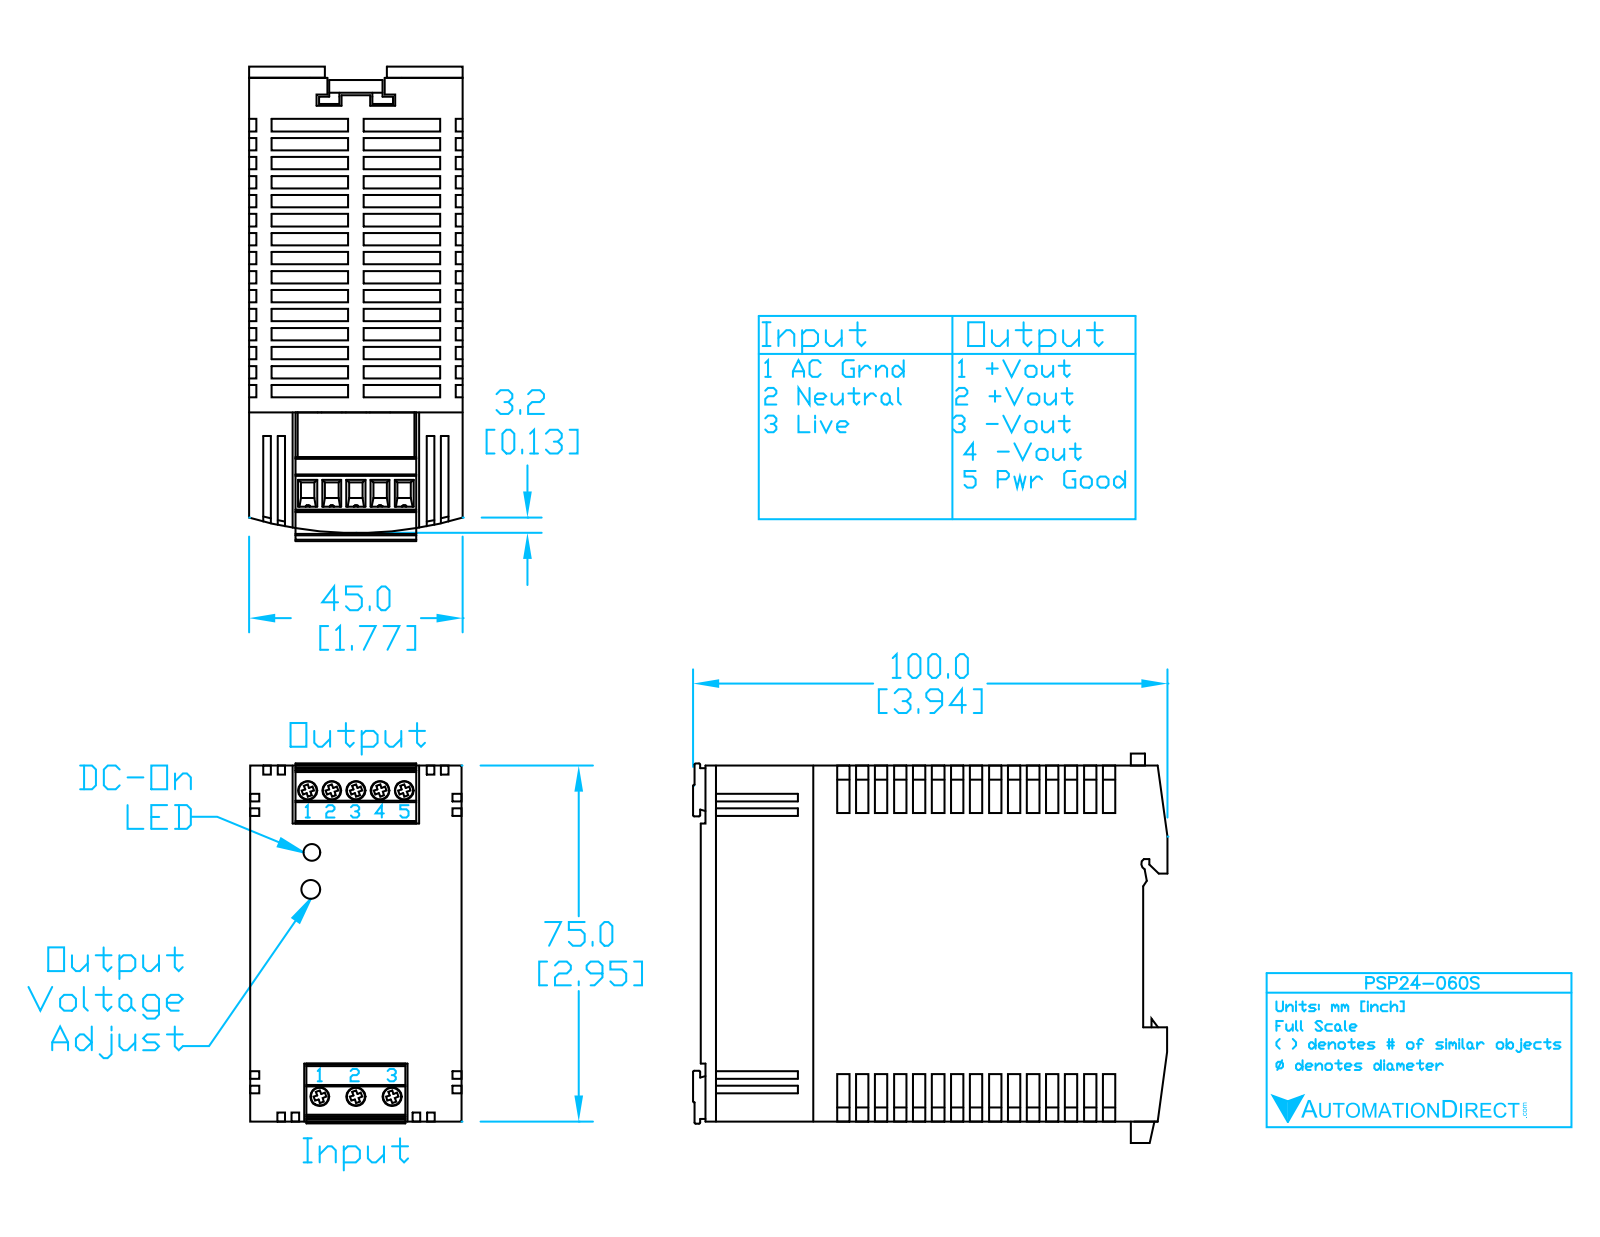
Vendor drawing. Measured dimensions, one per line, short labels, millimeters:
name: PSP24-060S
written by: SolidWorks 2011 (CONFIG_CONTROL_DESIGN)
unit: mm
bodies: 23 solids, 341 faces (272 planar, 0 cylindrical, 69 other)
size: 102.01 × 80 × 45
volume: 382 681 mm³; area: 61 399 mm²
face distances: 45, 75, 68.85, 14.36, 60.64, 2, 70.85, 2.37, 11.85, 12.25
